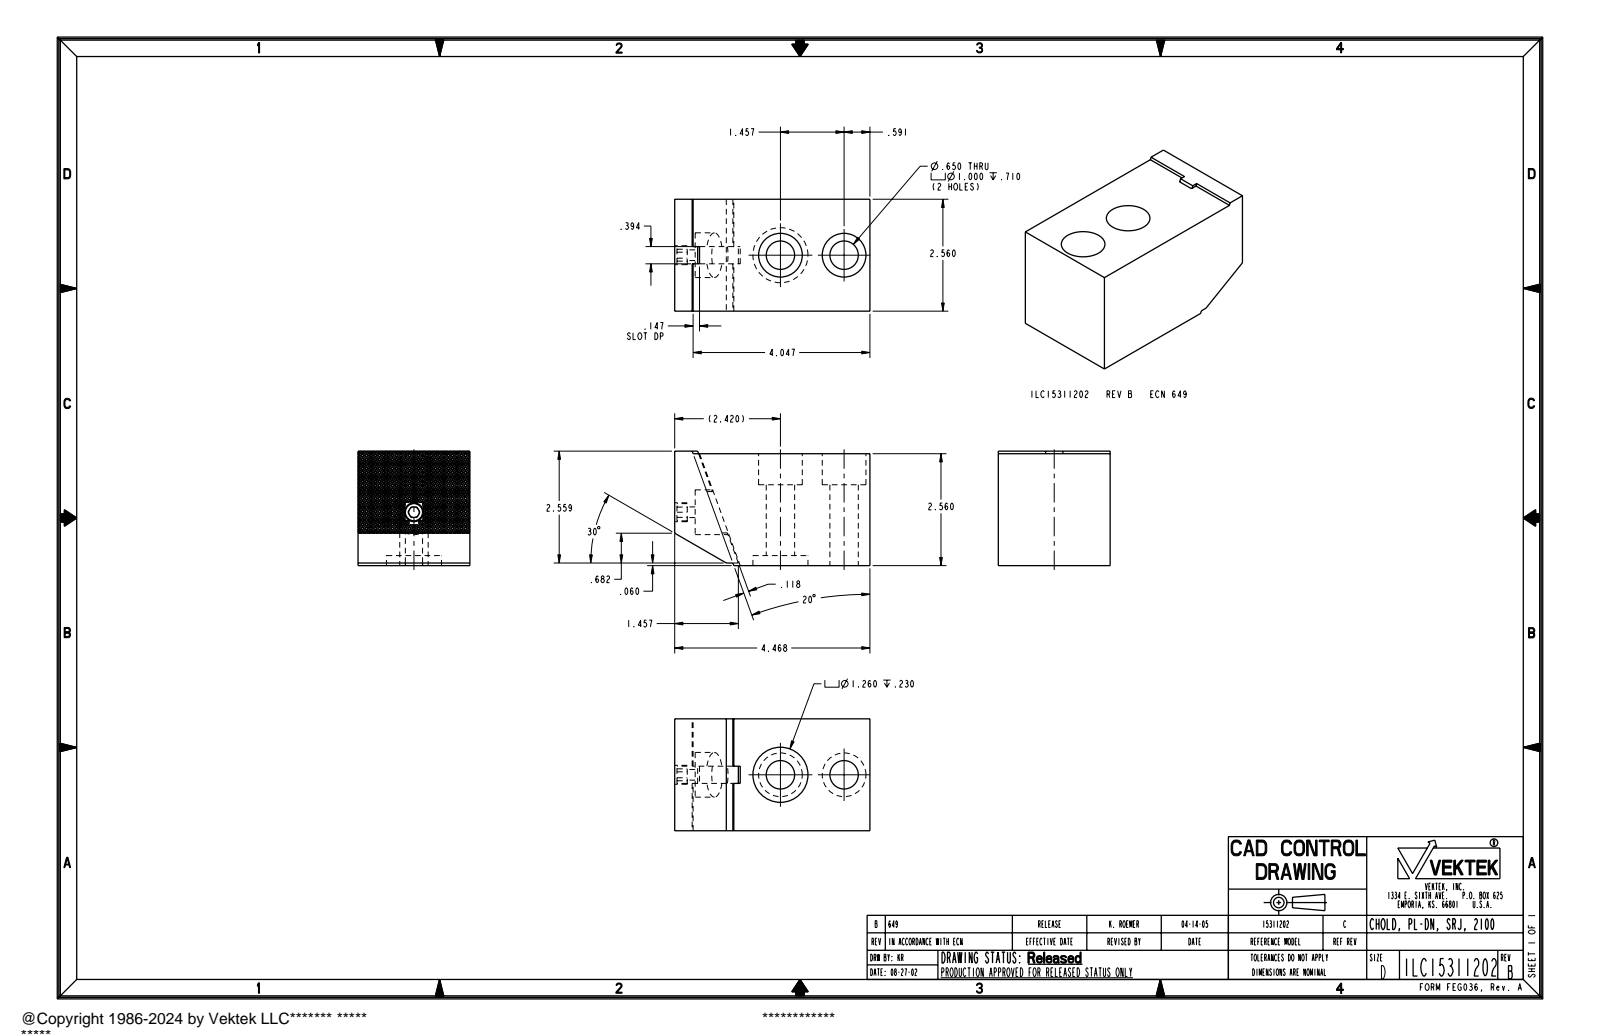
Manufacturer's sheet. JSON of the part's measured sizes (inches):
{"part_name": "ILC15311202", "step_written_by": "PRO/ENGINEER BY PARAMETRIC TECHNOLOGY CORPORATION, 2004290 (AUTOMOTIVE_DESIGN_CC2)", "units": "inches", "bodies": {"solids": 1, "faces": 64, "planar": 46, "cylindrical": 18, "other": 0}, "overall_size": [4.468, 2.619, 2.56], "volume_in3": 25.09, "surface_area_in2": 73.76, "round_holes": [[0.65, 2], [1, 2], [0.244, 1], [0.433, 1], [1.024, 1], [1.26, 1]], "round_bosses_or_shafts": [[0.394, 1]], "face_to_face_distances": [2.56, 4.468, 2.619, 0.059, 0.23, 2.33, 2.389, 1.85, 1.62, 0.71], "hole_center_spacings": [1.457]}
